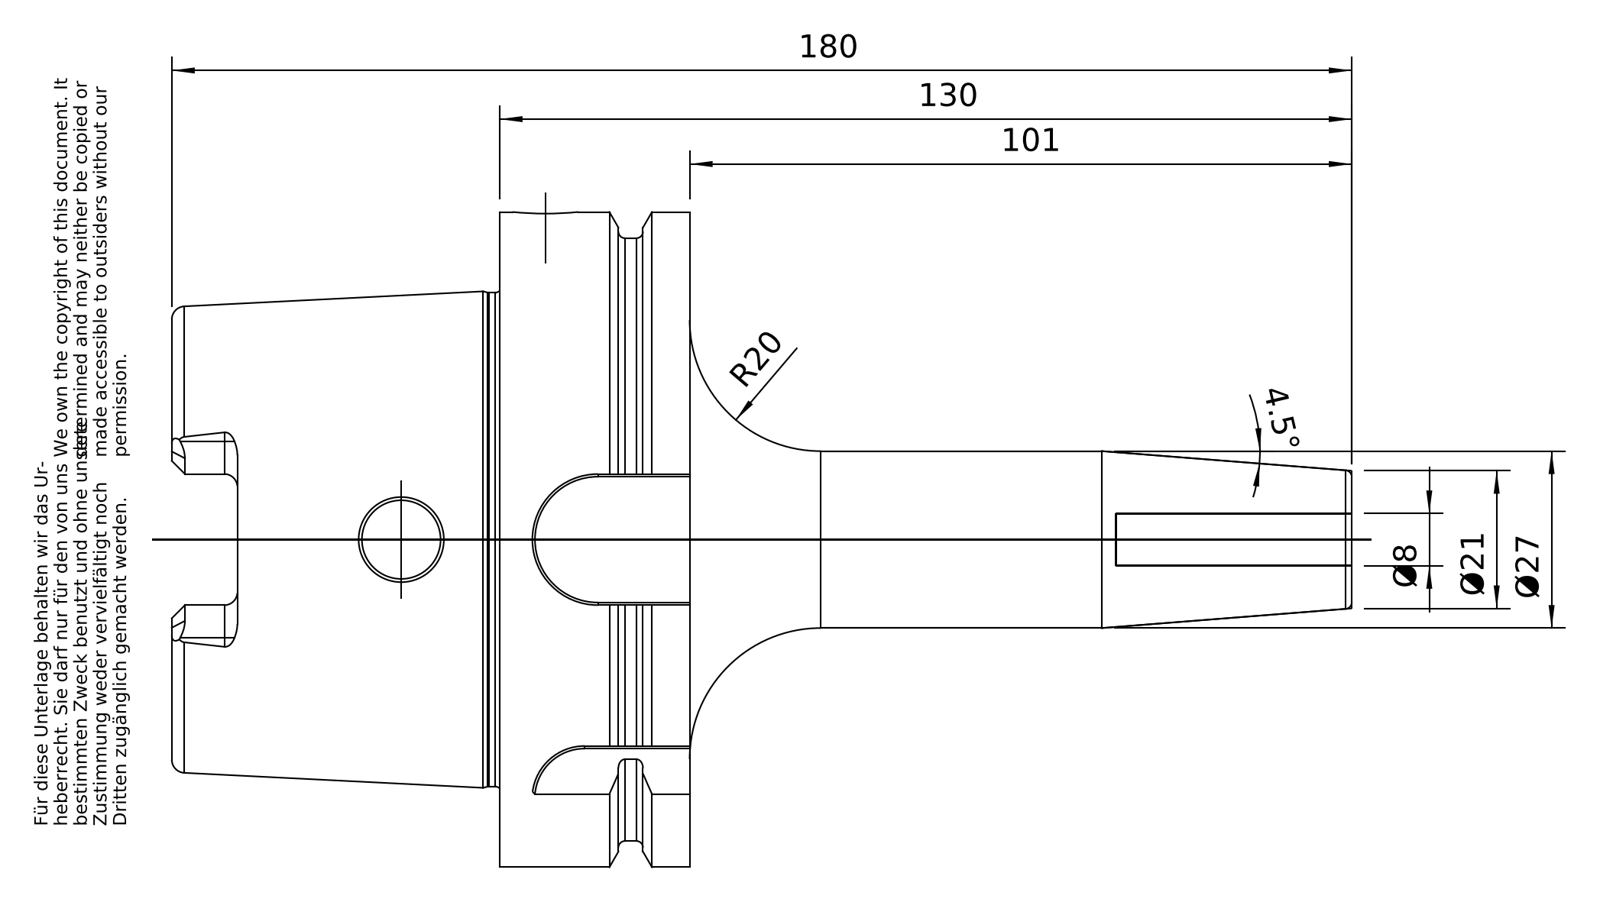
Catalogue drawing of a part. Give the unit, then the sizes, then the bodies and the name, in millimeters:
Units: millimetres
Overall size (bounding box): 180 × 100 × 100
Round holes (diameter × count): ⌀8 ×1, ⌀10 ×1, ⌀12 ×1, ⌀22.5 ×1, ⌀24 ×1, ⌀24.32 ×1, ⌀24.5 ×1, ⌀53 ×1, ⌀63 ×1
Round bosses / shafts (diameter × count): ⌀100 ×1, ⌀92 ×1, ⌀75.36 ×1, ⌀27 ×1
Partial cylindrical surfaces — rounded edges, fillets, slot ends (radius × count): R2 ×6, R5 ×4, R8 ×1, R10 ×1, R11 ×1
Main face-to-face distances: 29, 12.5, 16.5, 50, 62.5, 79, 88, 78.5, 28.5, 16
Volume: 315 417 mm³ · Surface area: 58 558 mm²
Bodies: 1 solid, 174 faces (50 planar, 51 cylindrical, 73 other)
Part name (STEP PRODUCT): A100-144-08
STEP written by: PRO/ENGINEER BY PARAMETRIC TECHNOLOGY CORPORATION, 2010430 (CONFIG_CONTROL_DESIGN)
